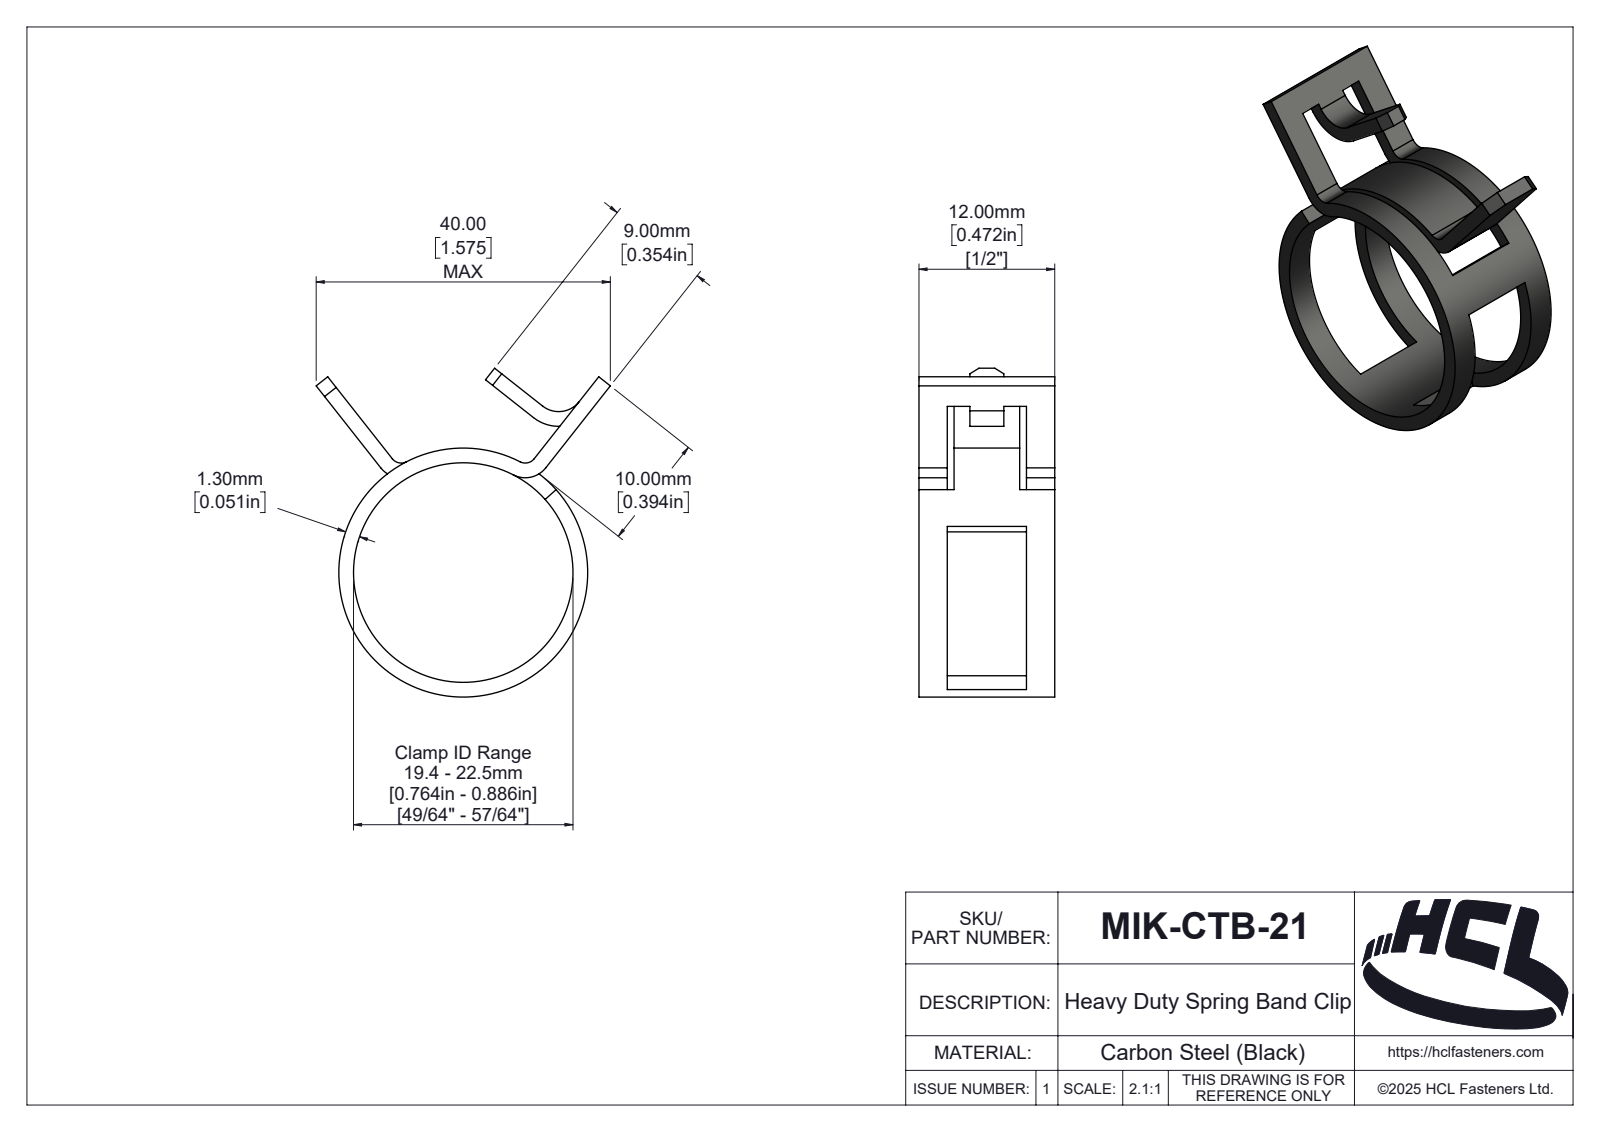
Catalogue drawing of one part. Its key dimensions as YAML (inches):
part_name: "MIK-CTB-21"
step_written_by: "SolidWorks 2025 (AUTOMOTIVE_DESIGN)"
units: inches
bodies: {solids: 1, faces: 149, planar: 36, cylindrical: 64, other: 49}
overall_size: [1.144, 1.024, 0.472]
volume: 0.052
surface_area: 2.835
round_holes:
  - {diameter: 0.764, count: 1}
round_bosses_or_shafts:
  - {diameter: 0.866, count: 1}
partial_cylinders:
  - {radius: 0.091, count: 3}
  - {radius: 0.039, count: 2}
  - {radius: 0.013, count: 1}
  - {radius: 0.053, count: 1}
  - {radius: 0.066, count: 1}
  - {radius: 0.07, count: 1}
  - {radius: 0.084, count: 1}
  - {radius: 0.119, count: 1}
face_to_face_distances: [0.098, 0.374, 0.051, 0.472, 0.252, 0.276, 0.122, 0.35, 0.024, 0.228]
